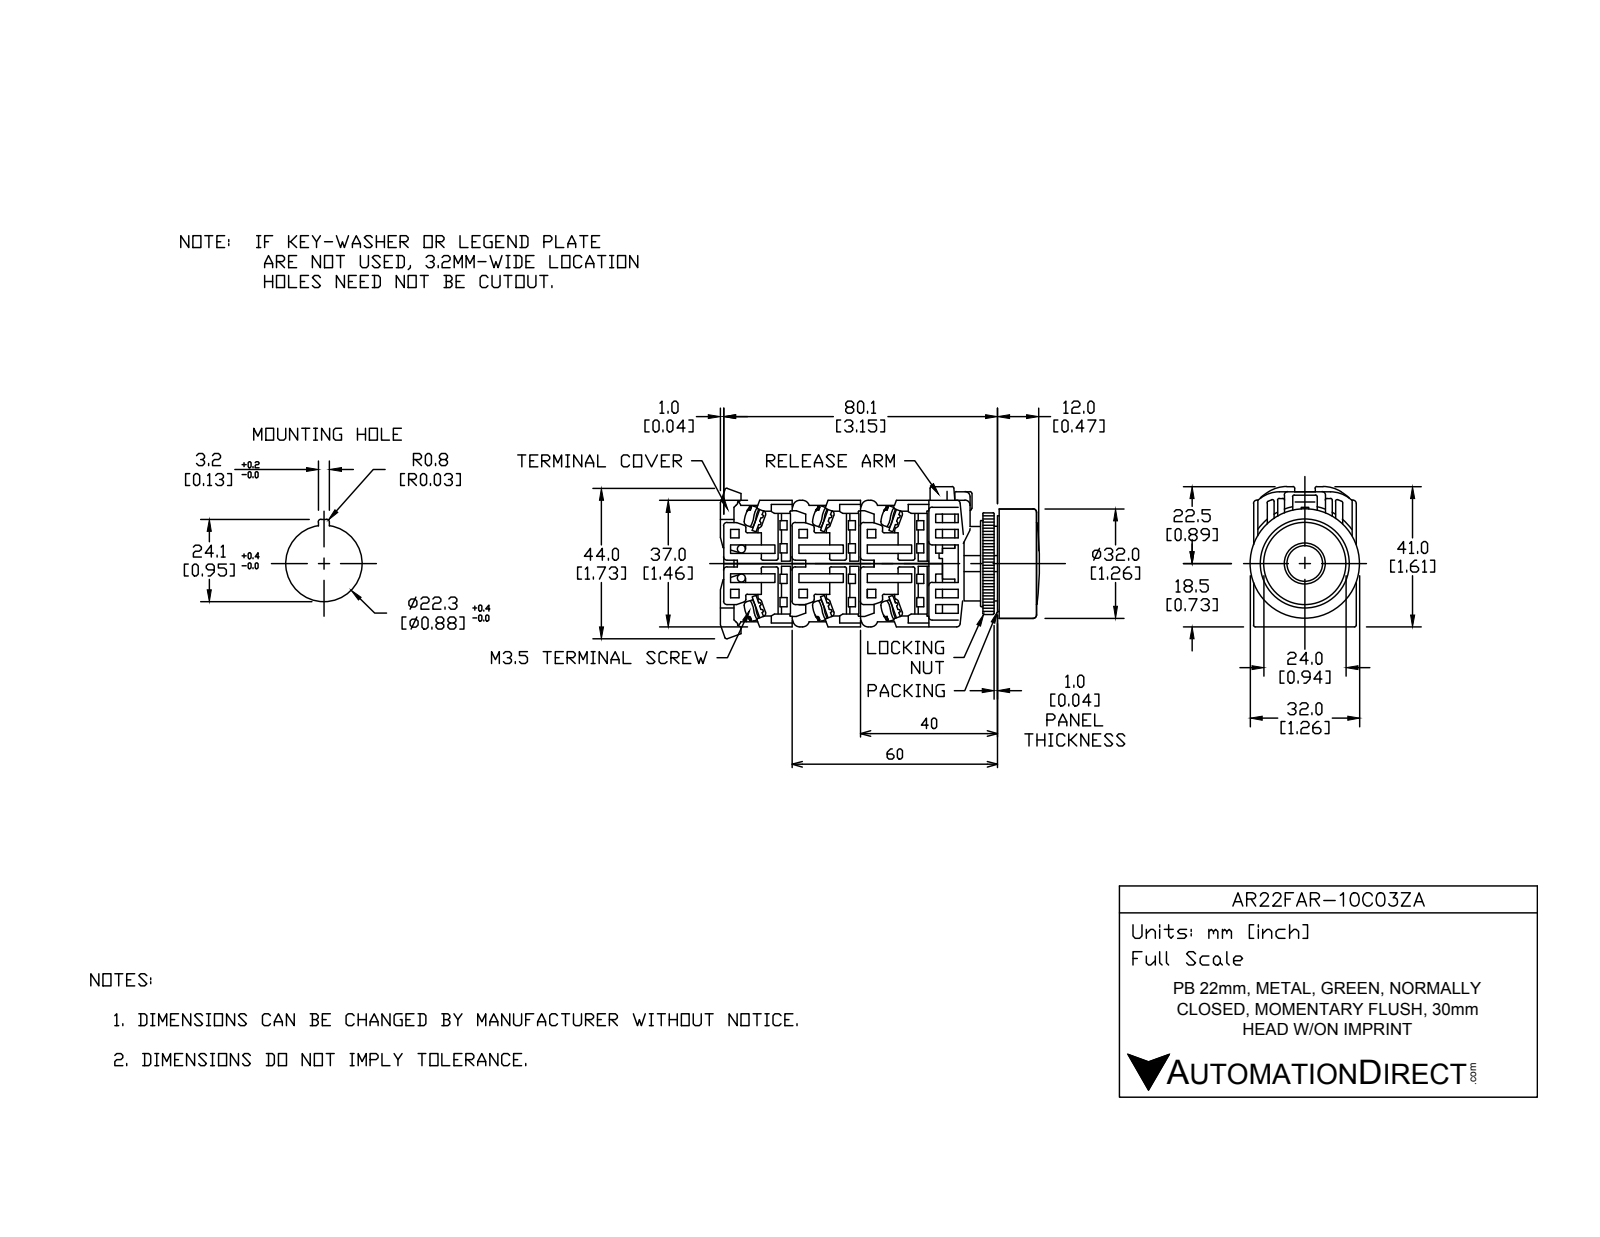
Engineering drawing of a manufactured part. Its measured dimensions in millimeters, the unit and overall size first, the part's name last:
Units: millimetres
Overall size (bounding box): 52.75 × 41 × 32
Round holes (diameter × count): ⌀21.8 ×1, ⌀22 ×1, ⌀25 ×1, ⌀31 ×1
Round bosses / shafts (diameter × count): ⌀5 ×2, ⌀32 ×1, ⌀30.5 ×1, ⌀29.8 ×1, ⌀24 ×1, ⌀23.8 ×1, ⌀21.75 ×1, ⌀17 ×1
Partial cylindrical surfaces — rounded edges, fillets, slot ends (radius × count): R0.5 ×23, R1.75 ×4, R5 ×4, R4 ×2, R16.59 ×1, R17.59 ×1
Main face-to-face distances: 1, 28.5, 18, 3, 2, 29, 30, 10.5, 8, 20.5
Volume: 27 343 mm³ · Surface area: 19 392 mm²
Bodies: 12 solids, 301 faces (205 planar, 74 cylindrical, 22 other)
Part name (STEP PRODUCT): AR22FAR-10C03ZA
STEP written by: SolidWorks 2017 (AUTOMOTIVE_DESIGN)
